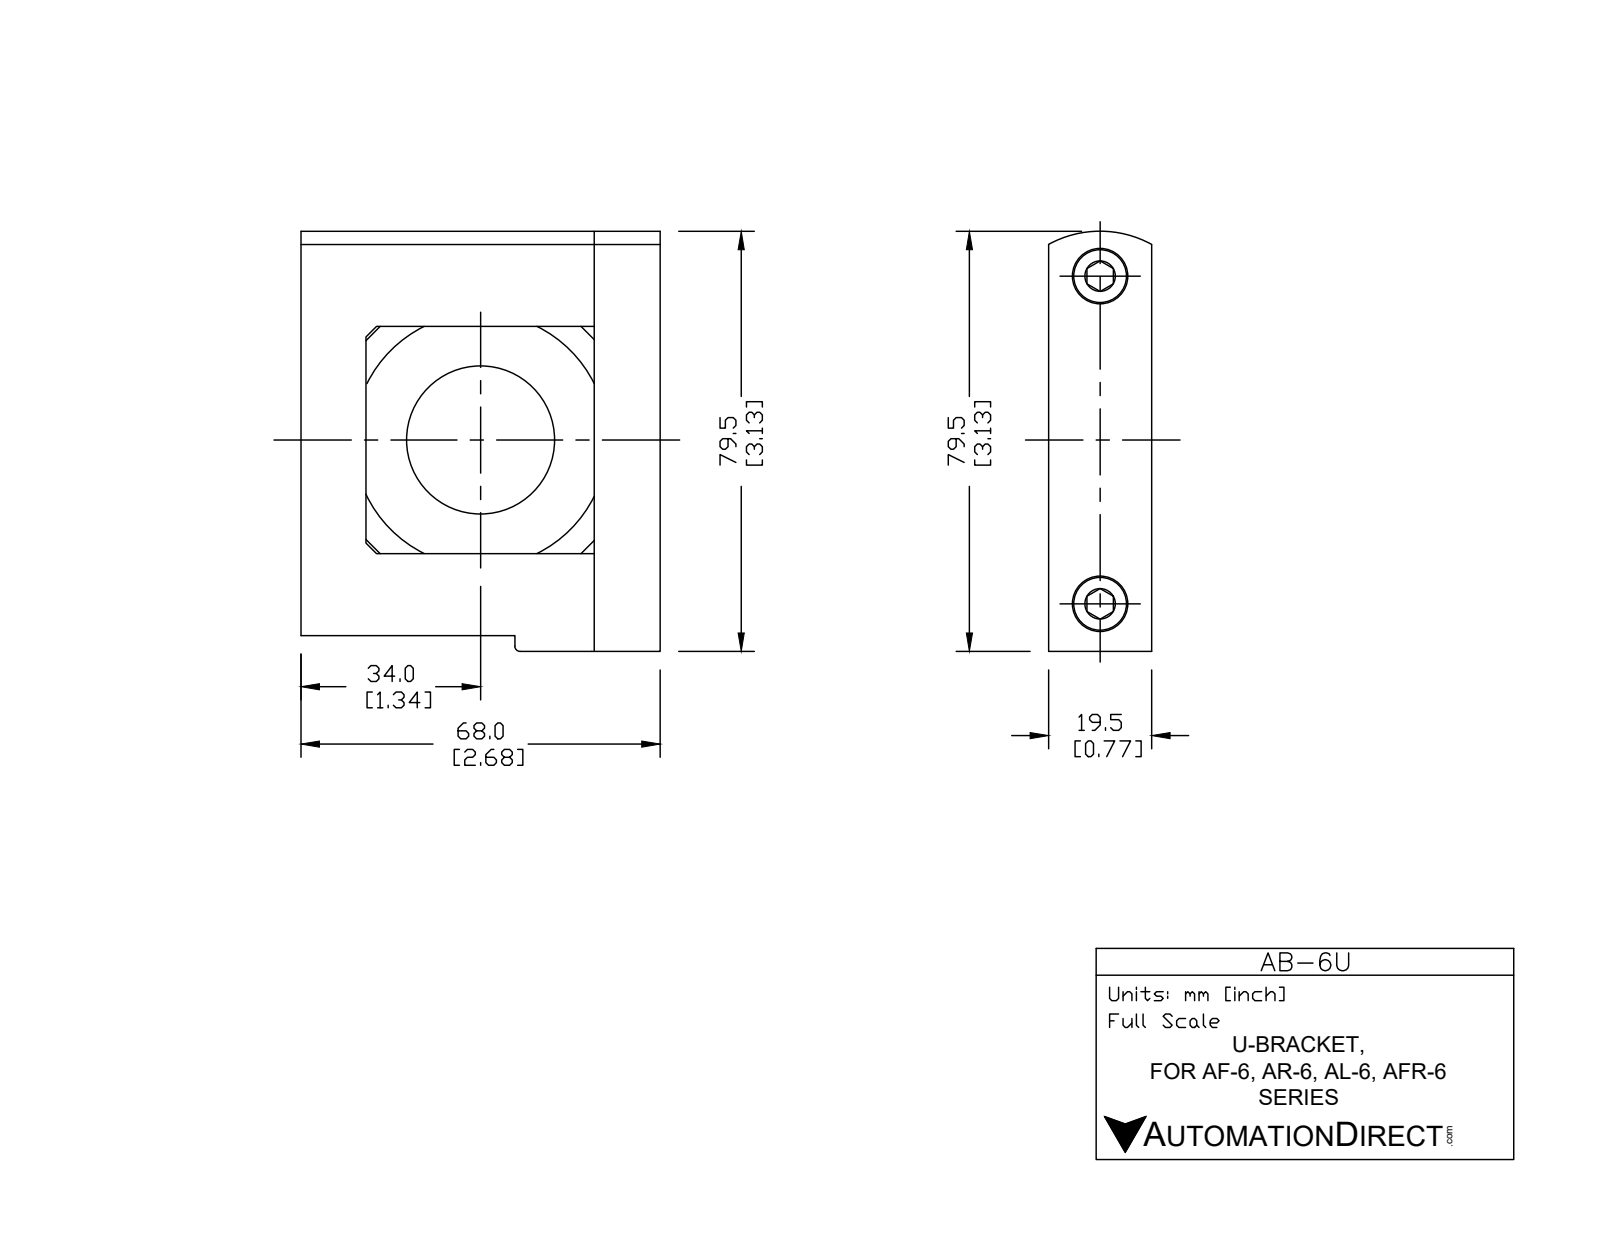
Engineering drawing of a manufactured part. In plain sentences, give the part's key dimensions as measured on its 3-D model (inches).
The part is named "AB-6U". Its 3-D file was written by "SolidWorks 2015 (CONFIG_CONTROL_DESIGN)". It is 3 solids with 92 faces: 60 planar, 20 cylindrical and 12 other. Overall it measures 3.13 by 2.677 by 0.768 inches. Its volume is 3.92 cubic inches and its surface area 34.78 square inches. Round holes: 2 of diameter 0.256, 2 of diameter 0.415, 1 of diameter 1.102. Round bosses or shafts: 2 of diameter 0.384, 2 of diameter 0.157. Partial cylindrical surfaces (rounded edges, fillets, slot ends): 1 of radius 0.059, 1 of radius 0.798. The main face-to-face distances are 0.768, 0.118, 2.677, 1.811, 0.492, 2.303, 0.374, 0.352, 0.416, 2.185. The hole center spacings are 2.441.
